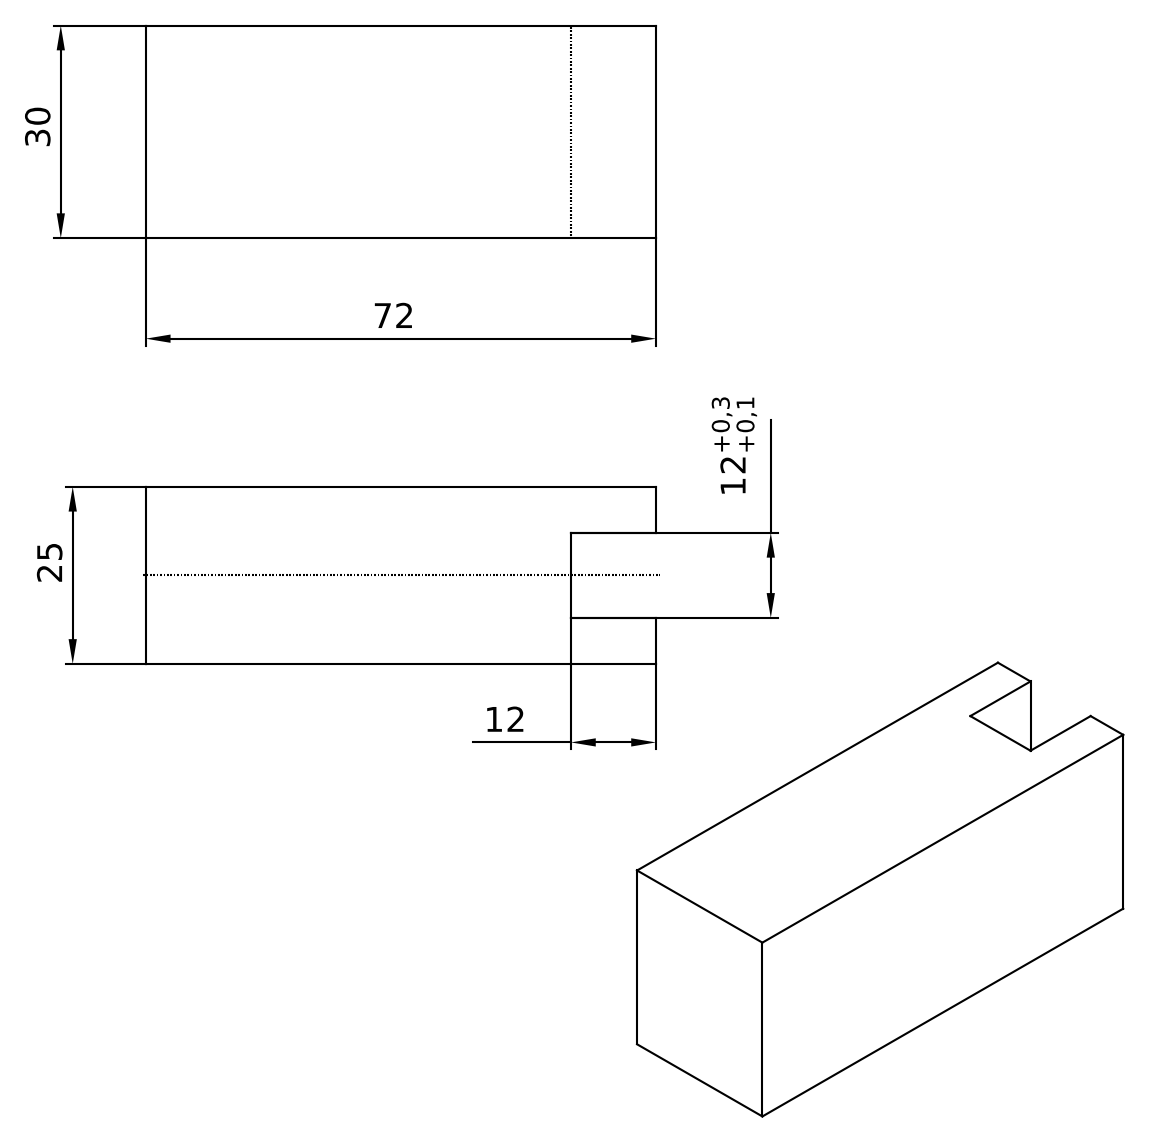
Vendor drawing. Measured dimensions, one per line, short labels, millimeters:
name: 605-21E1
written by: Autodesk Inventor 8 (AUTOMOTIVE_DESIGN)
unit: mm
bodies: 1 solid, 10 faces (10 planar, 0 cylindrical, 0 other)
size: 72 × 30 × 25
volume: 49 680 mm³; area: 9 852 mm²
face distances: 25, 30, 6.5, 18.5, 12, 72, 60
